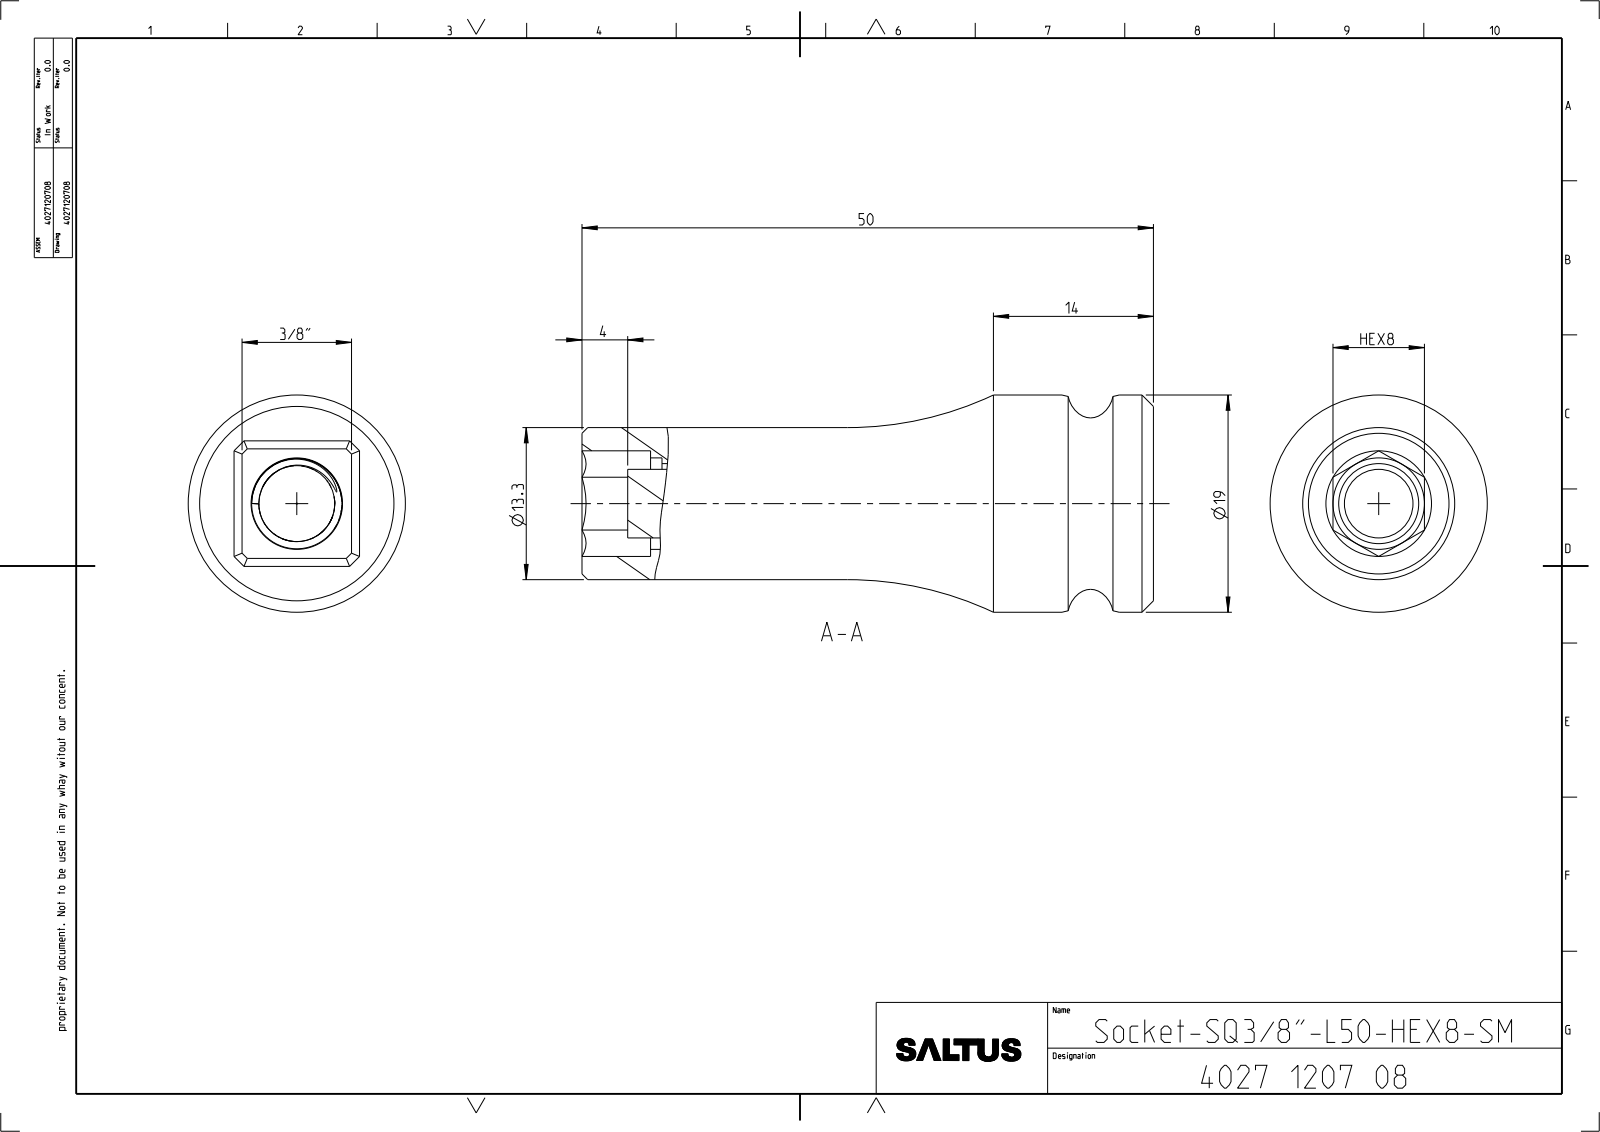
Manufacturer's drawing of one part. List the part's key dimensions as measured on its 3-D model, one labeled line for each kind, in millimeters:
Part name (STEP PRODUCT): 4027120708_ASM
STEP written by: CREO PARAMETRIC BY PTC INC, 2022414 (CONFIG_CONTROL_DESIGN)
Units: millimetres
Bodies: 1 solid, 77 faces (39 planar, 20 cylindrical, 18 other)
Overall size (bounding box): 50 × 19 × 19
Volume: 6 550 mm³ · Surface area: 4 682 mm²
Round holes (diameter × count): ⌀5 ×1, ⌀7 ×1, ⌀8 ×1
Round bosses / shafts (diameter × count): ⌀19 ×1, ⌀13.3 ×1, ⌀6 ×1
Main face-to-face distances: 9.58, 8, 0.79, 8.79, 50, 36, 14, 12, 24, 38
